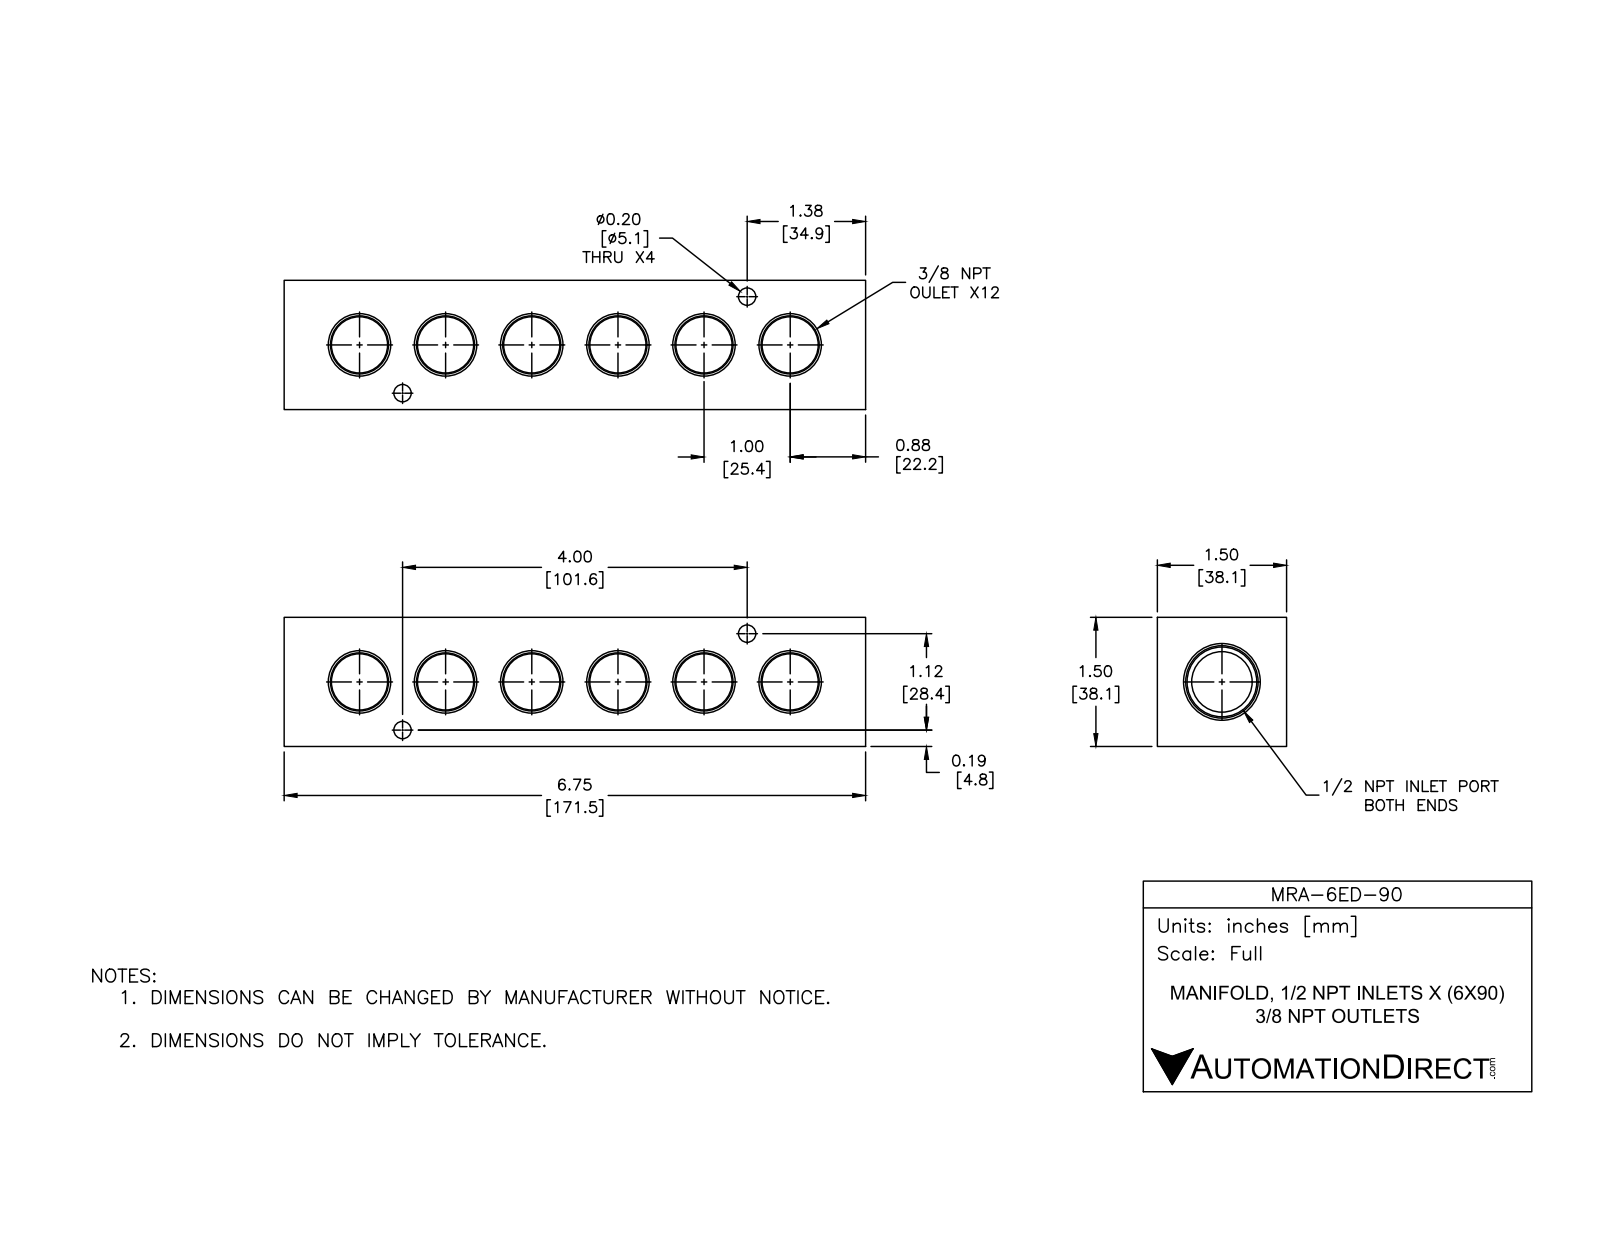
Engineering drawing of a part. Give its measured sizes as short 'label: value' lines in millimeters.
name: MRA-6ED-90
written by: SolidWorks 2015 (CONFIG_CONTROL_DESIGN)
unit: mm
bodies: 1 solid, 130 faces (32 planar, 42 cylindrical, 56 other)
size: 171.5 × 38.1 × 38.1
volume: 171 400 mm³; area: 42 990 mm²
holes: 12× ⌀14.3, 4× ⌀5.1, 1× ⌀17.9
face distances: 38.1, 171.5, 27.7, 10.4, 13.5, 158, 144.5
hole spacings: 25.4, 19.1, 50.8, 76.2, 40.7, 65.1, 90, 101.6
